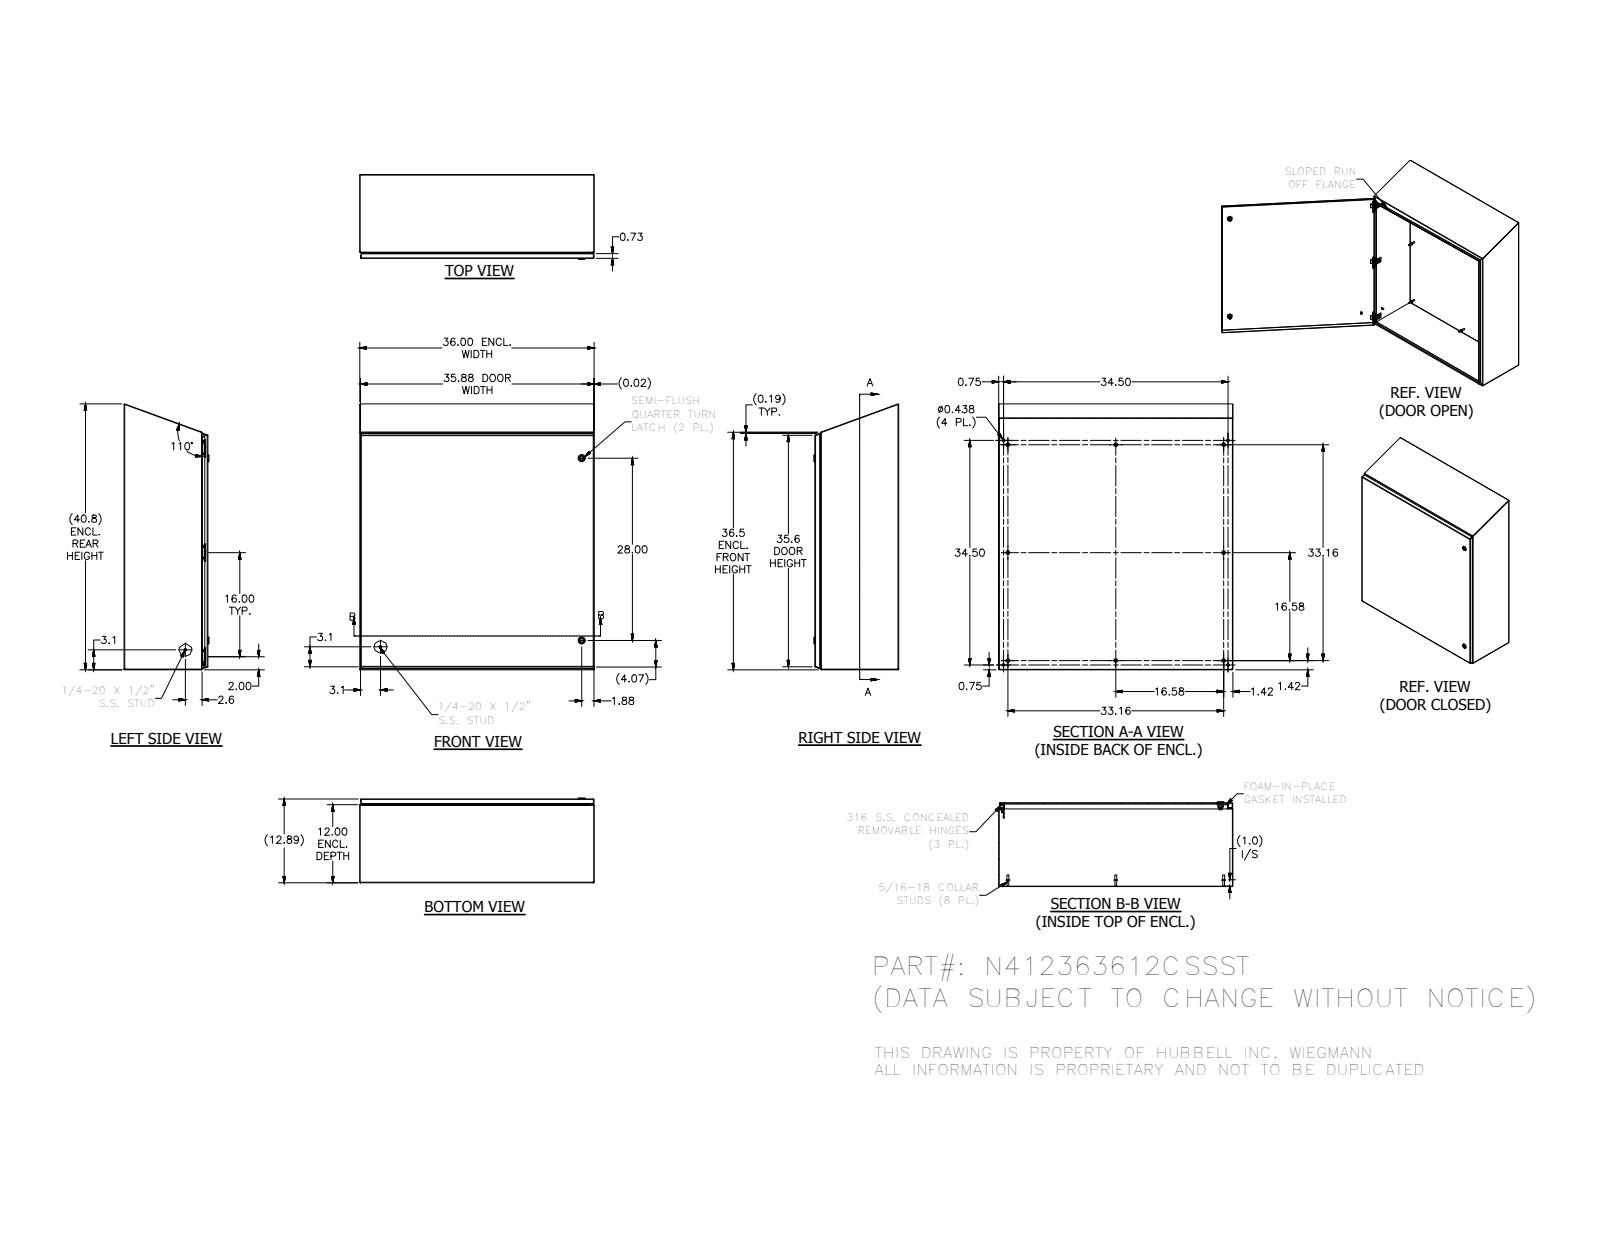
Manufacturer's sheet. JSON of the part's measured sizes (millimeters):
{"part_name": "N412_CSSST-assm; N412363612CSSSTB3S; HFW3161; HFW328176 (+8 more)", "step_written_by": "Autodesk Inventor 2012 (AUTOMOTIVE_DESIGN)", "units": "millimeters", "bodies": {"solids": 55, "faces": 2184, "planar": 850, "cylindrical": 788, "other": 546}, "overall_size": [1037.5, 914.4, 331.3], "volume_mm3": 5929000, "surface_area_mm2": 6336000, "round_holes": [[2.4, 6], [3.9, 6], [4.2, 6], [4.4, 6], [4.7, 6], [4, 4], [11.1, 4], [5, 2], [8, 2], [10, 2], [10.2, 2], [16.1, 2]], "round_bosses_or_shafts": [[6.4, 14], [14.3, 8], [7.6, 8], [7, 8], [9.1, 6], [8.1, 6], [6.5, 6], [4.2, 6]], "partial_cylinders_radius": [[1.3, 38], [0.8, 33], [0.4, 26], [0.5, 24], [3.2, 24], [2.7, 19], [0.8, 12], [13.3, 8]], "face_to_face_distances": [1.9, 325.5, 323.6, 327.3, 912.5, 910.6, 914.4, 302.9, 22.5, 20.7], "hole_center_spacings": [406.4, 812.8, 406.6, 876.3, 12.7, 16.7, 16.8, 33.2]}
